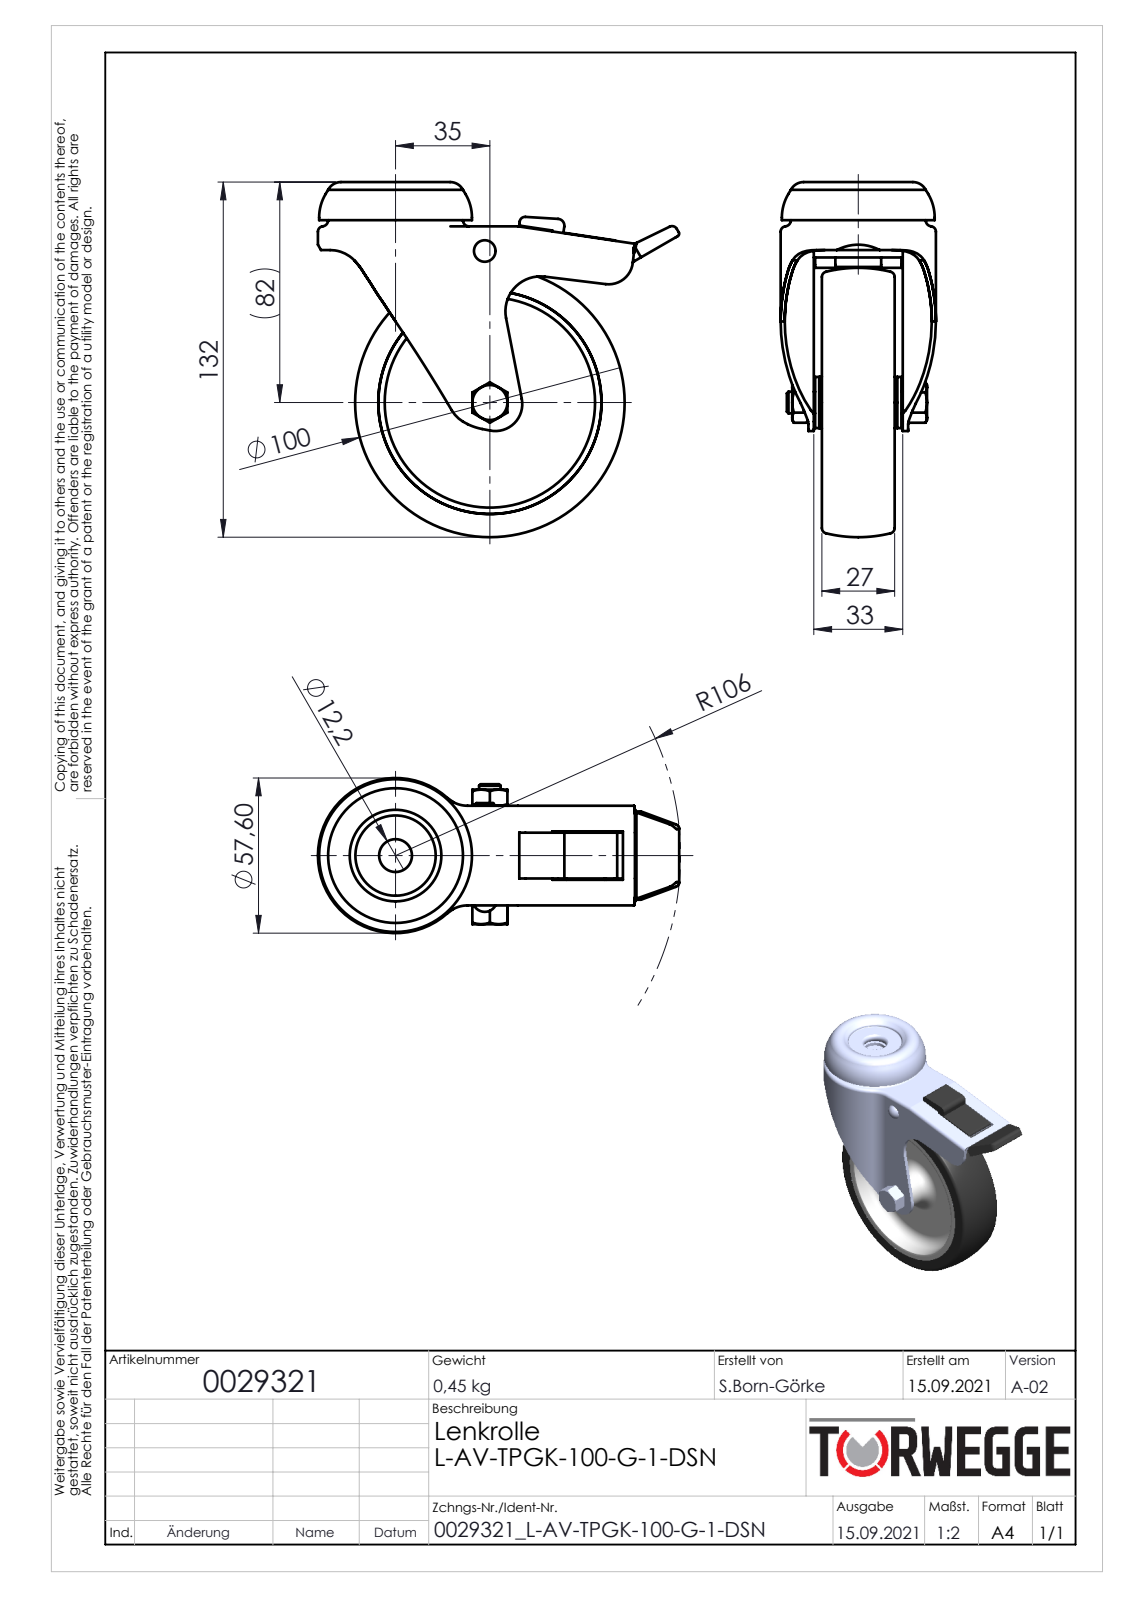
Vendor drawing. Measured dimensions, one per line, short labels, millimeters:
name: 0029321
written by: SolidWorks 2020 (AUTOMOTIVE_DESIGN)
unit: mm
bodies: 9 solids, 916 faces (660 planar, 108 cylindrical, 148 other)
size: 134.04 × 131.85 × 78.8
volume: 183 436 mm³; area: 98 751 mm²
holes: 2× ⌀12.3, 1× ⌀3, 1× ⌀4.8, 1× ⌀6.8, 1× ⌀8, 1× ⌀8.2, 1× ⌀12.6, 1× ⌀15.56, 1× ⌀82.8, 1× ⌀92
bosses: 1× ⌀56.7, 1× ⌀45.15, 1× ⌀19, 1× ⌀6.8
rounds: 7× R2, 3× R1, 2× R3, 2× R6, 2× R11, 1× R0.3, 1× R0.5, 1× R0.75
face distances: 2, 5, 14.25, 18.75, 32, 11.25, 3, 30, 15.75, 16.25
hole spacings: 56.28
